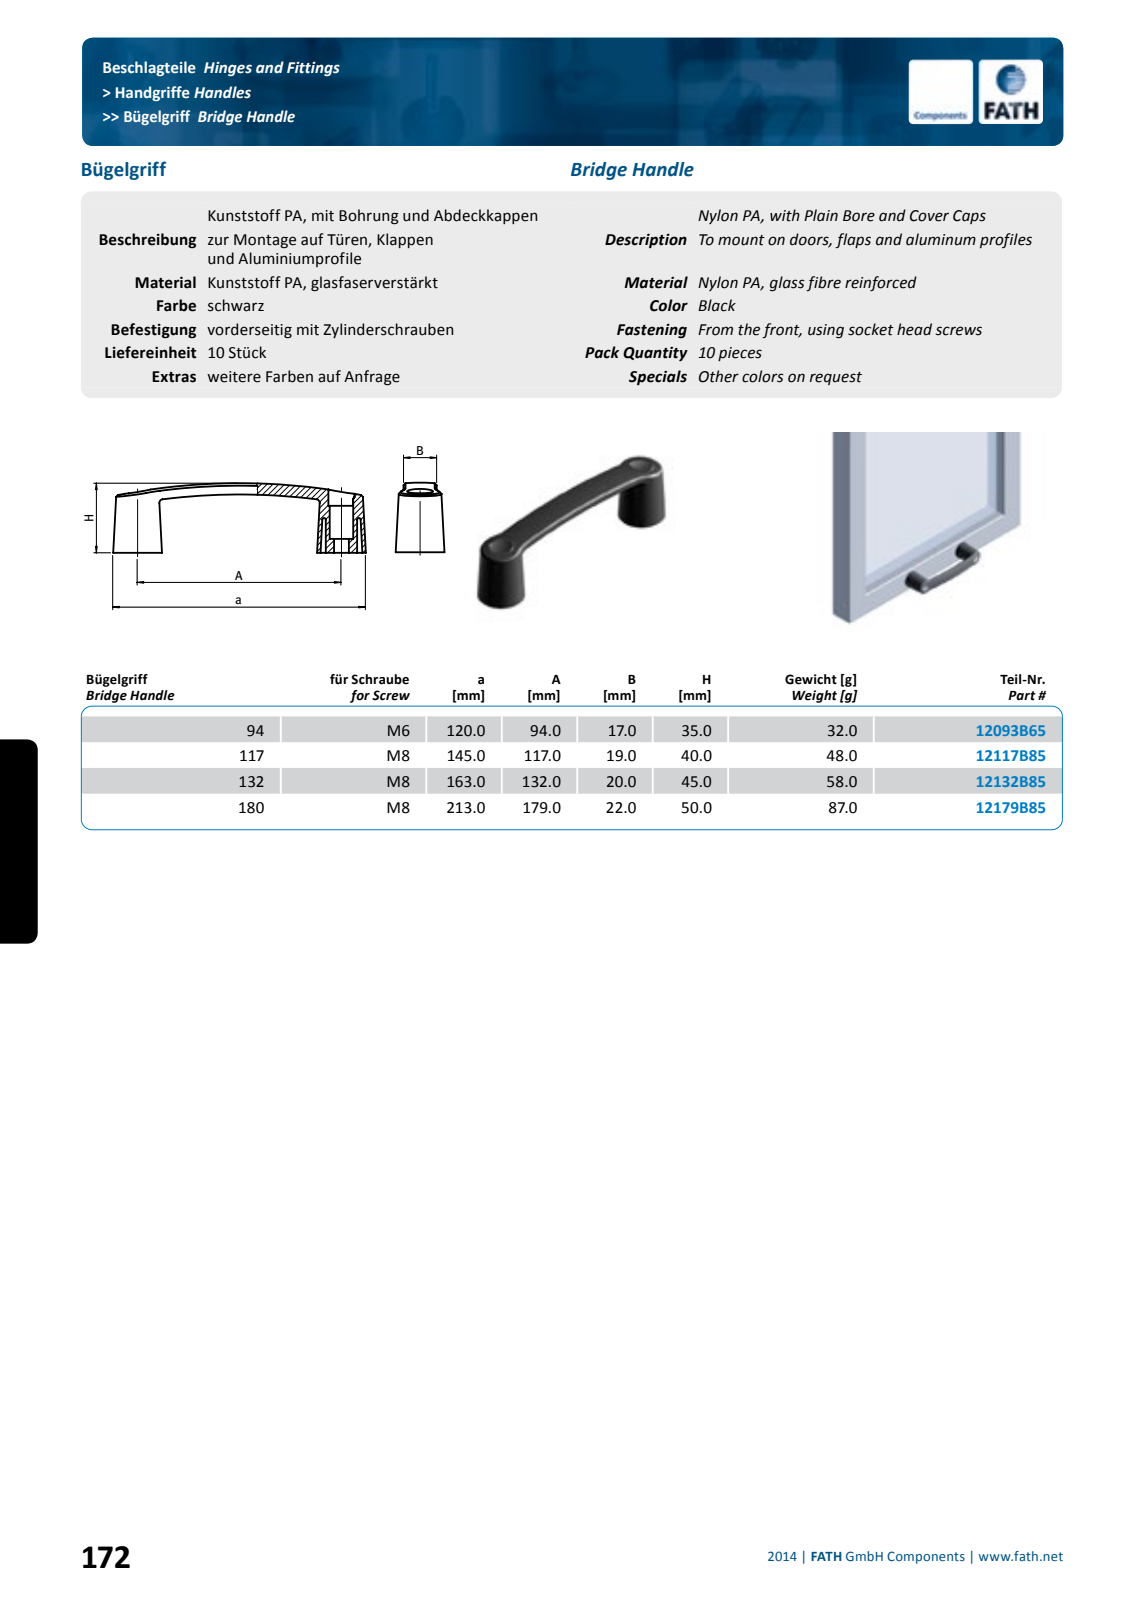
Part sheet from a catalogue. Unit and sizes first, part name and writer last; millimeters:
Units: millimetres
Overall size (bounding box): 213 × 50 × 35
Round holes (diameter × count): ⌀9 ×2, ⌀13.7 ×2, ⌀17 ×2
Main face-to-face distances: 22, 12.3, 34, 21.7, 62.76
Hole centre spacings: 178
Volume: 78 445 mm³ · Surface area: 22 607 mm²
Bodies: 1 solid, 58 faces (12 planar, 14 cylindrical, 32 other)
Part name (STEP PRODUCT): fath_12179b85
STEP written by: Spatial InterOp 3D (automotive_design)
